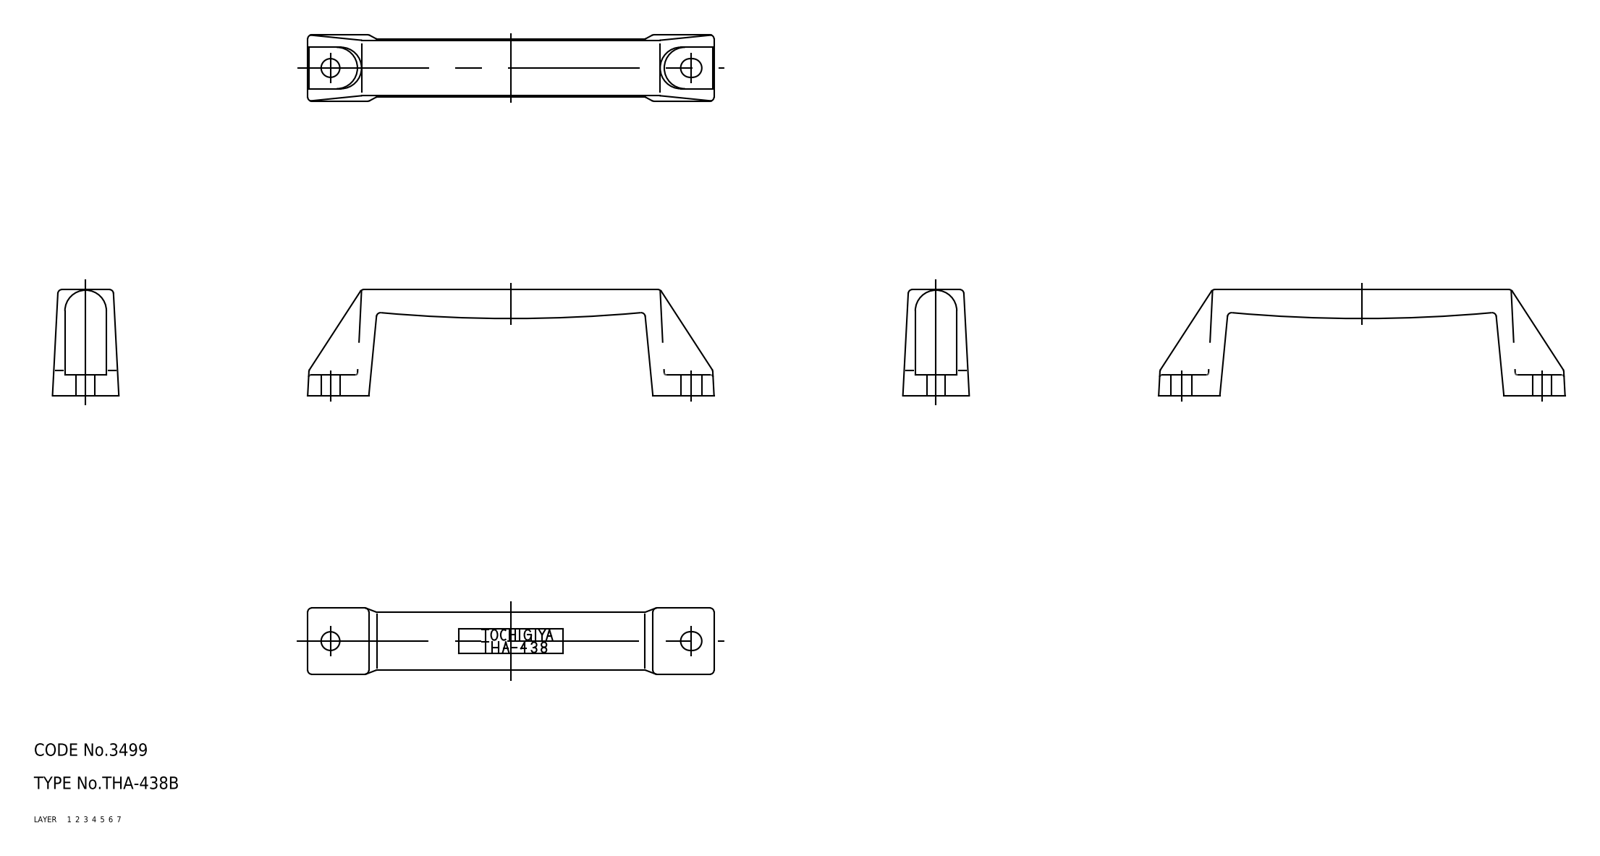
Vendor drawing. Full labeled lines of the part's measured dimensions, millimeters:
Part name (STEP PRODUCT): 67112864
STEP written by: CADfix (AUTOMOTIVE_DESIGN)
Units: millimetres
Bodies: 1 solid, 76 faces (0 planar, 0 cylindrical, 76 other)
Overall size (bounding box): 98 × 25.6 × 16
Volume: 11 586 mm³ · Surface area: 6 098 mm²
